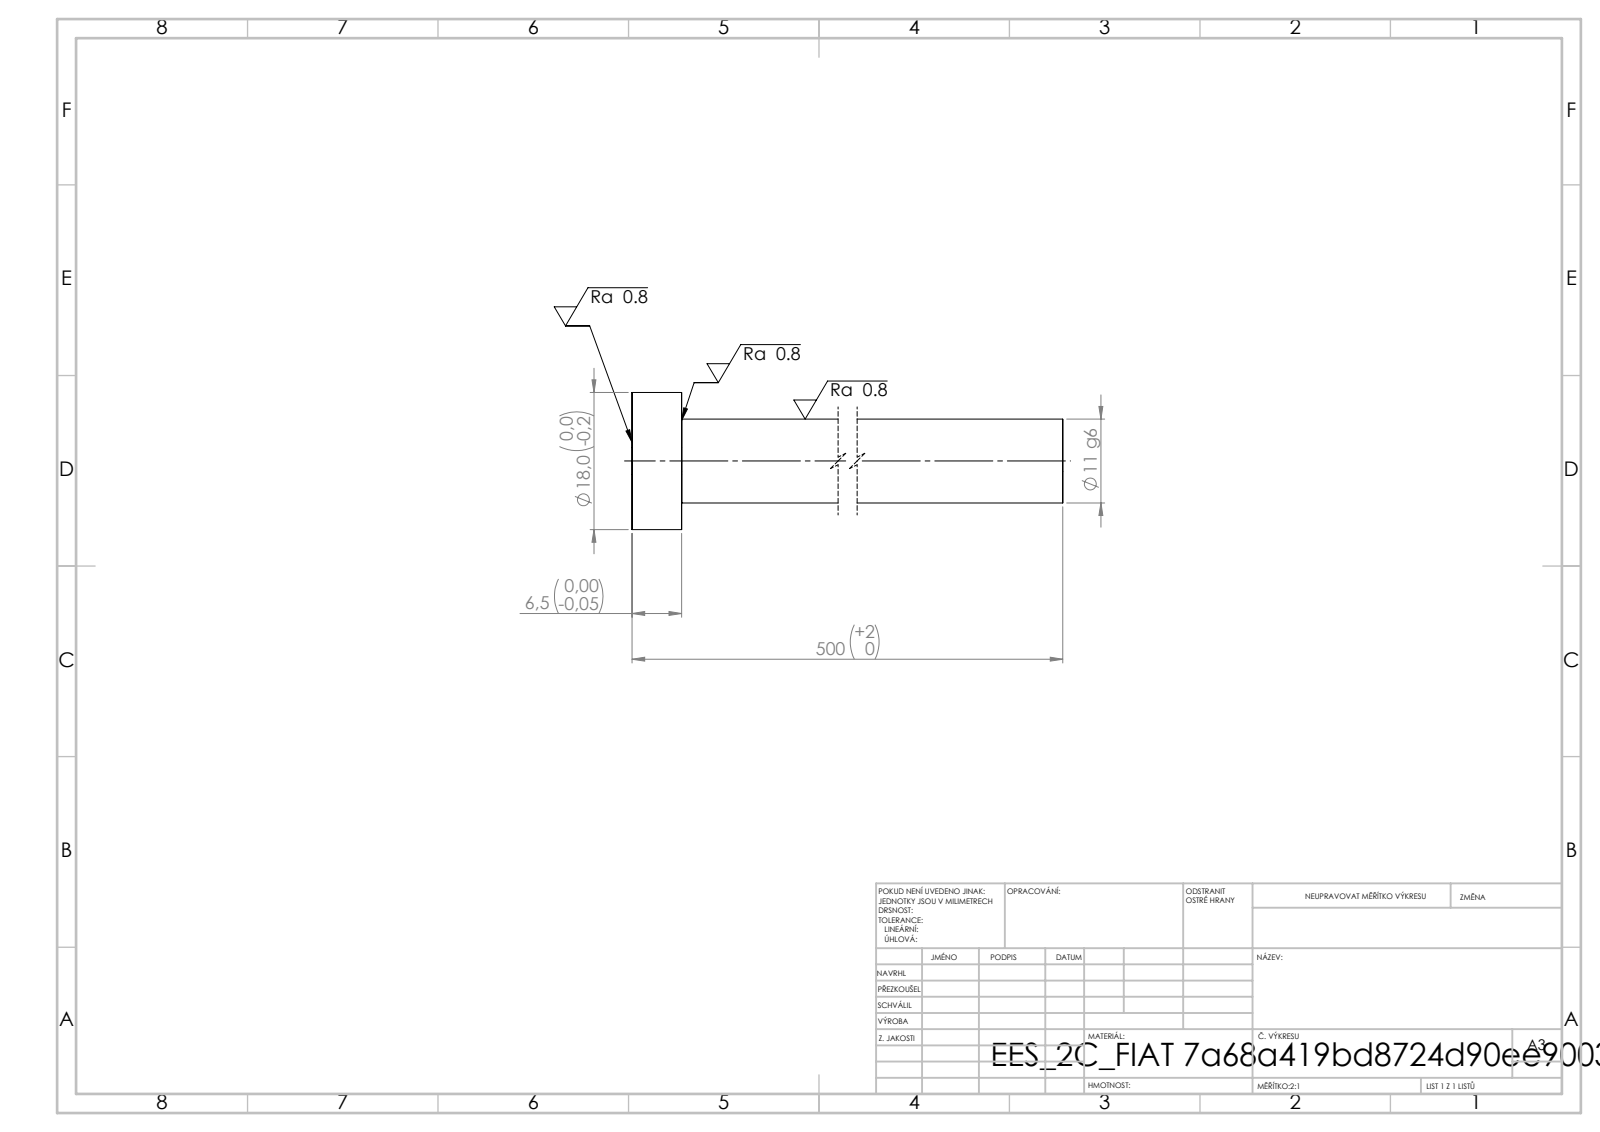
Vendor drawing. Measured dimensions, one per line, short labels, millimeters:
written by: SolidWorks 2019 (CONFIG_CONTROL_DESIGN)
unit: mm
bodies: 1 solid, 7 faces (3 planar, 4 cylindrical, 0 other)
size: 500 × 18 × 18
volume: 48 553 mm³; area: 17 931 mm²
bosses: 1× ⌀18, 1× ⌀11
face distances: 6.5, 500, 493.5
